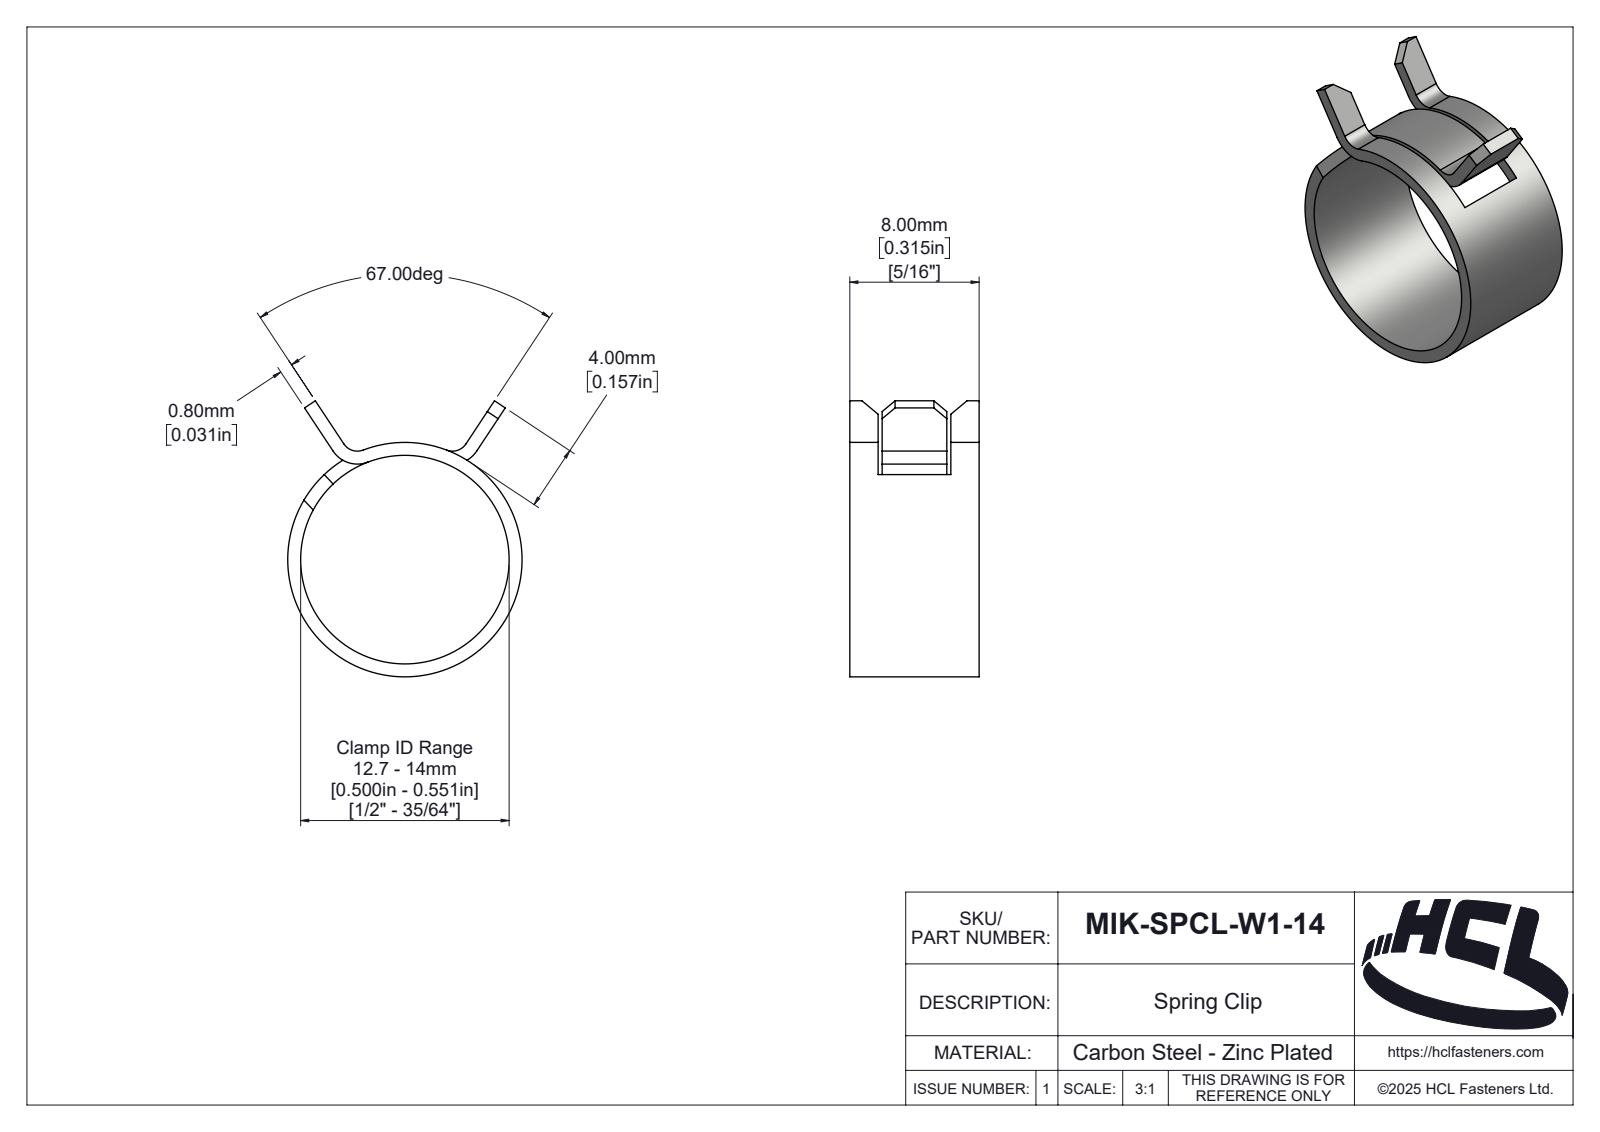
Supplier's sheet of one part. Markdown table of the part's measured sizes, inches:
| quantity | value |
| --- | --- |
| part name | MIK-SPCL-W1-14 |
| STEP written by | SolidWorks 2025 (AUTOMOTIVE_DESIGN) |
| units | inches |
| bodies | 1 solid, 135 faces (24 planar, 62 cylindrical, 49 other) |
| overall size | 0.672 × 0.571 × 0.315 |
| volume | 0.017 in³ |
| surface area | 1.29 in² |
| round holes (diameter × count) | 0.508 × 1 |
| round bosses / shafts (diameter × count) | 0.571 × 1 |
| partial cylindrical surfaces (radius × count) | 0.039 × 2, 0.071 × 2, 0.009 × 1, 0.037 × 1, 0.046 × 1, 0.049 × 1, 0.059 × 1, 0.083 × 1 |
| main face-to-face distances | 0.315, 0.031, 0.079, 0.236, 0.069, 0.246, 0.167, 0.157, 0.177 |
